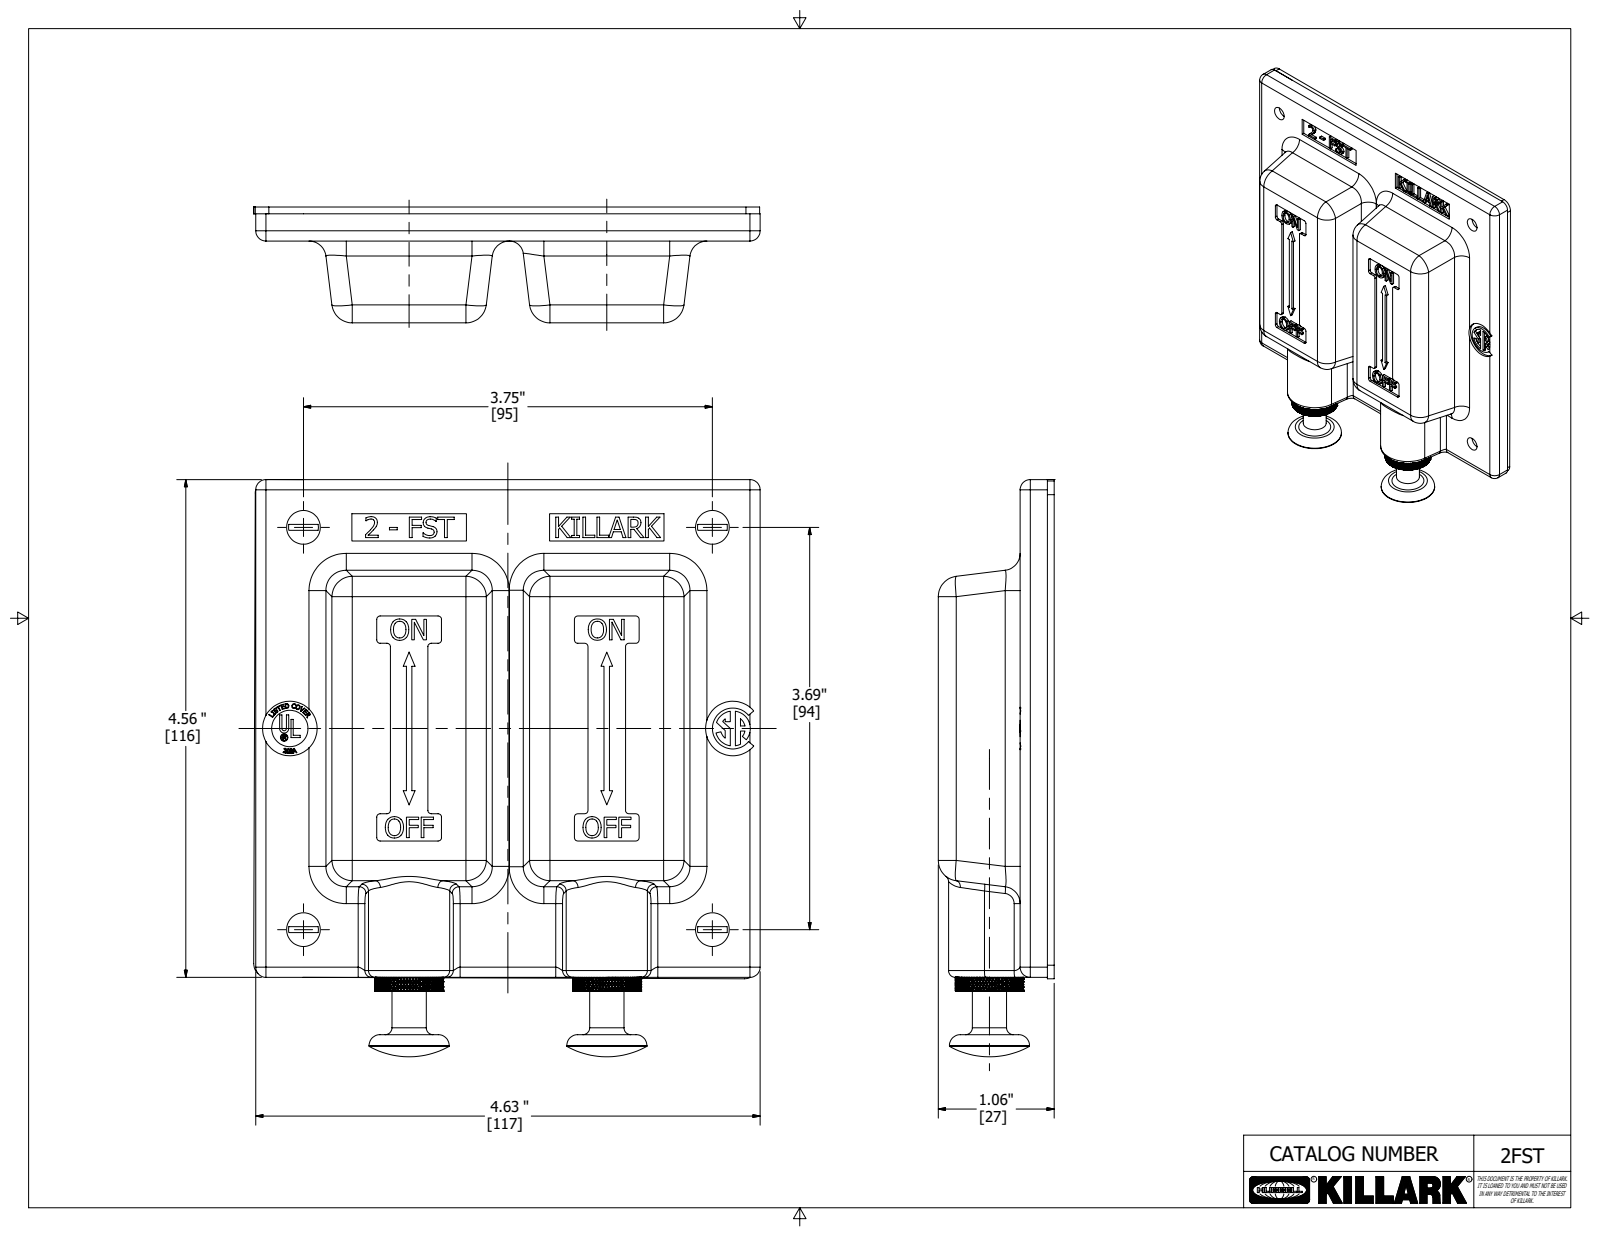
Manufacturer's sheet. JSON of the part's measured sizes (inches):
{"part_name": "02877BAAM; 0067640M; 0301400B; 0722675B (+4 more)", "step_written_by": "Autodesk Inventor 2020 (AUTOMOTIVE_DESIGN)", "units": "inches", "bodies": {"solids": 16, "faces": 7231, "planar": 5462, "cylindrical": 1234, "other": 535}, "overall_size": [5.292, 4.644, 1.43], "volume_in3": 6.445, "surface_area_in2": 107.6, "round_holes": [[0.187, 7], [0.156, 2], [0.22, 2], [0.313, 2], [0.324, 2], [0.332, 2], [0.422, 2], [0.453, 2], [0.5, 1]], "round_bosses_or_shafts": [[0.164, 4], [0.734, 2], [0.625, 2], [0.496, 2], [0.437, 2], [0.314, 2], [0.213, 2], [0.333, 1]], "partial_cylinders_radius": [[0.187, 29], [0.031, 24], [0.062, 24], [0.125, 12], [0.047, 10], [0.375, 10], [0.094, 8], [0.281, 6]], "face_to_face_distances": [0.75, 0.063, 0.25, 0.313, 0.125, 1, 0.139, 1.8, 0.625, 1.063], "hole_center_spacings": [3.687, 1.848, 4.291, 5.259, 3.75, 3.75, 5.267, 0.026]}
